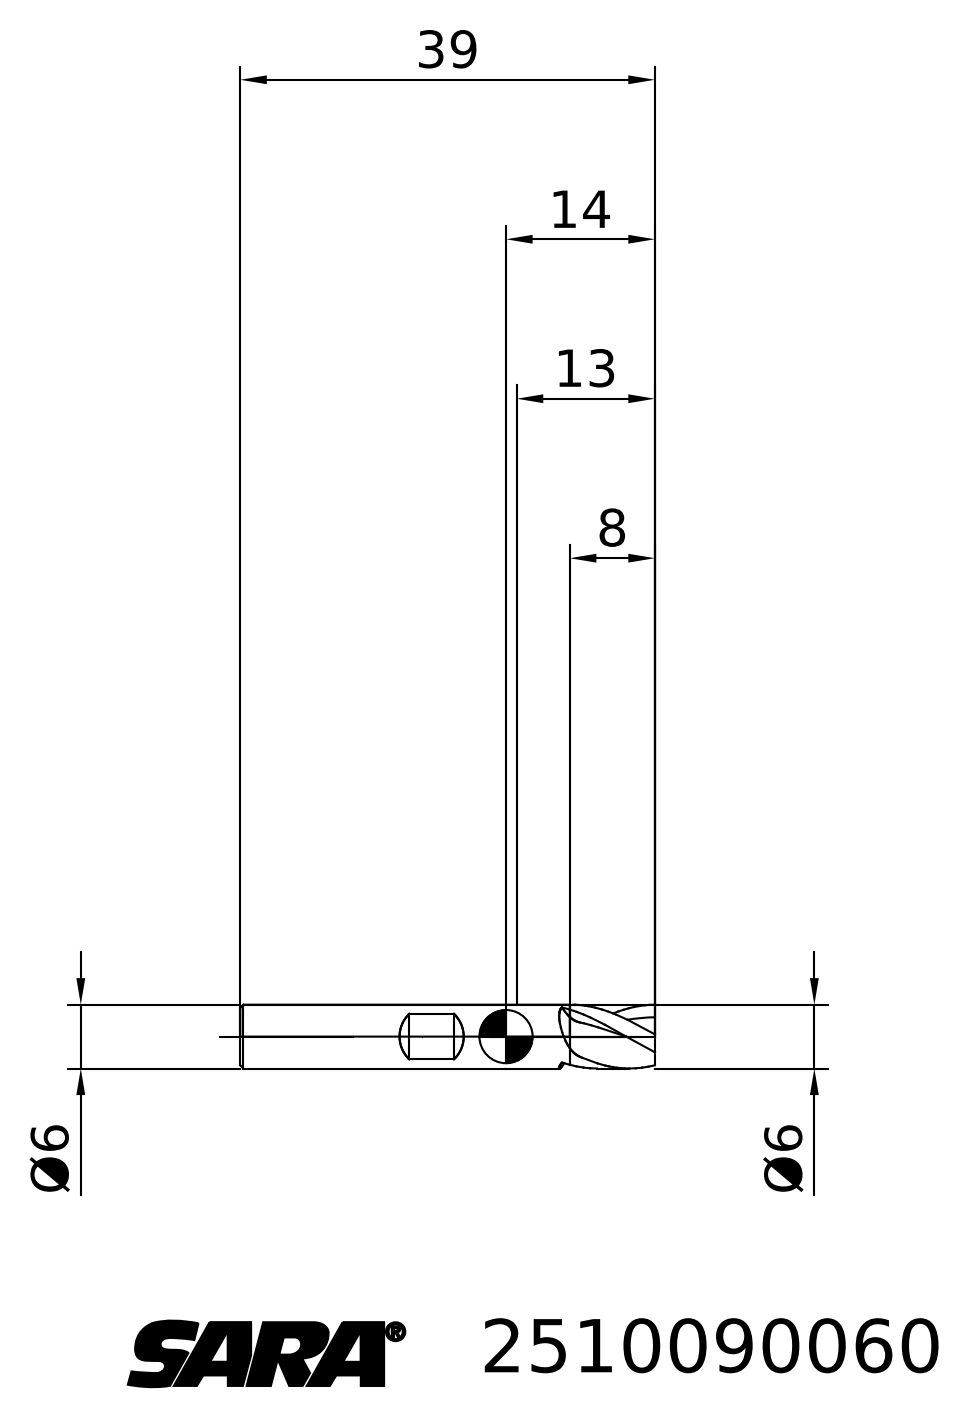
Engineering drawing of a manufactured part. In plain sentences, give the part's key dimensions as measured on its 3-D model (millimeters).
Its 3-D file was written by "TDM (AUTOMOTIVE_DESIGN)". It is 2 solids with 25 faces: 7 planar, 0 cylindrical and 18 other. Overall it measures 39 by 6 by 6 millimeters. Its volume is 987 cubic millimeters and its surface area 826 square millimeters. The main face-to-face distances are 31, 8, 39.
